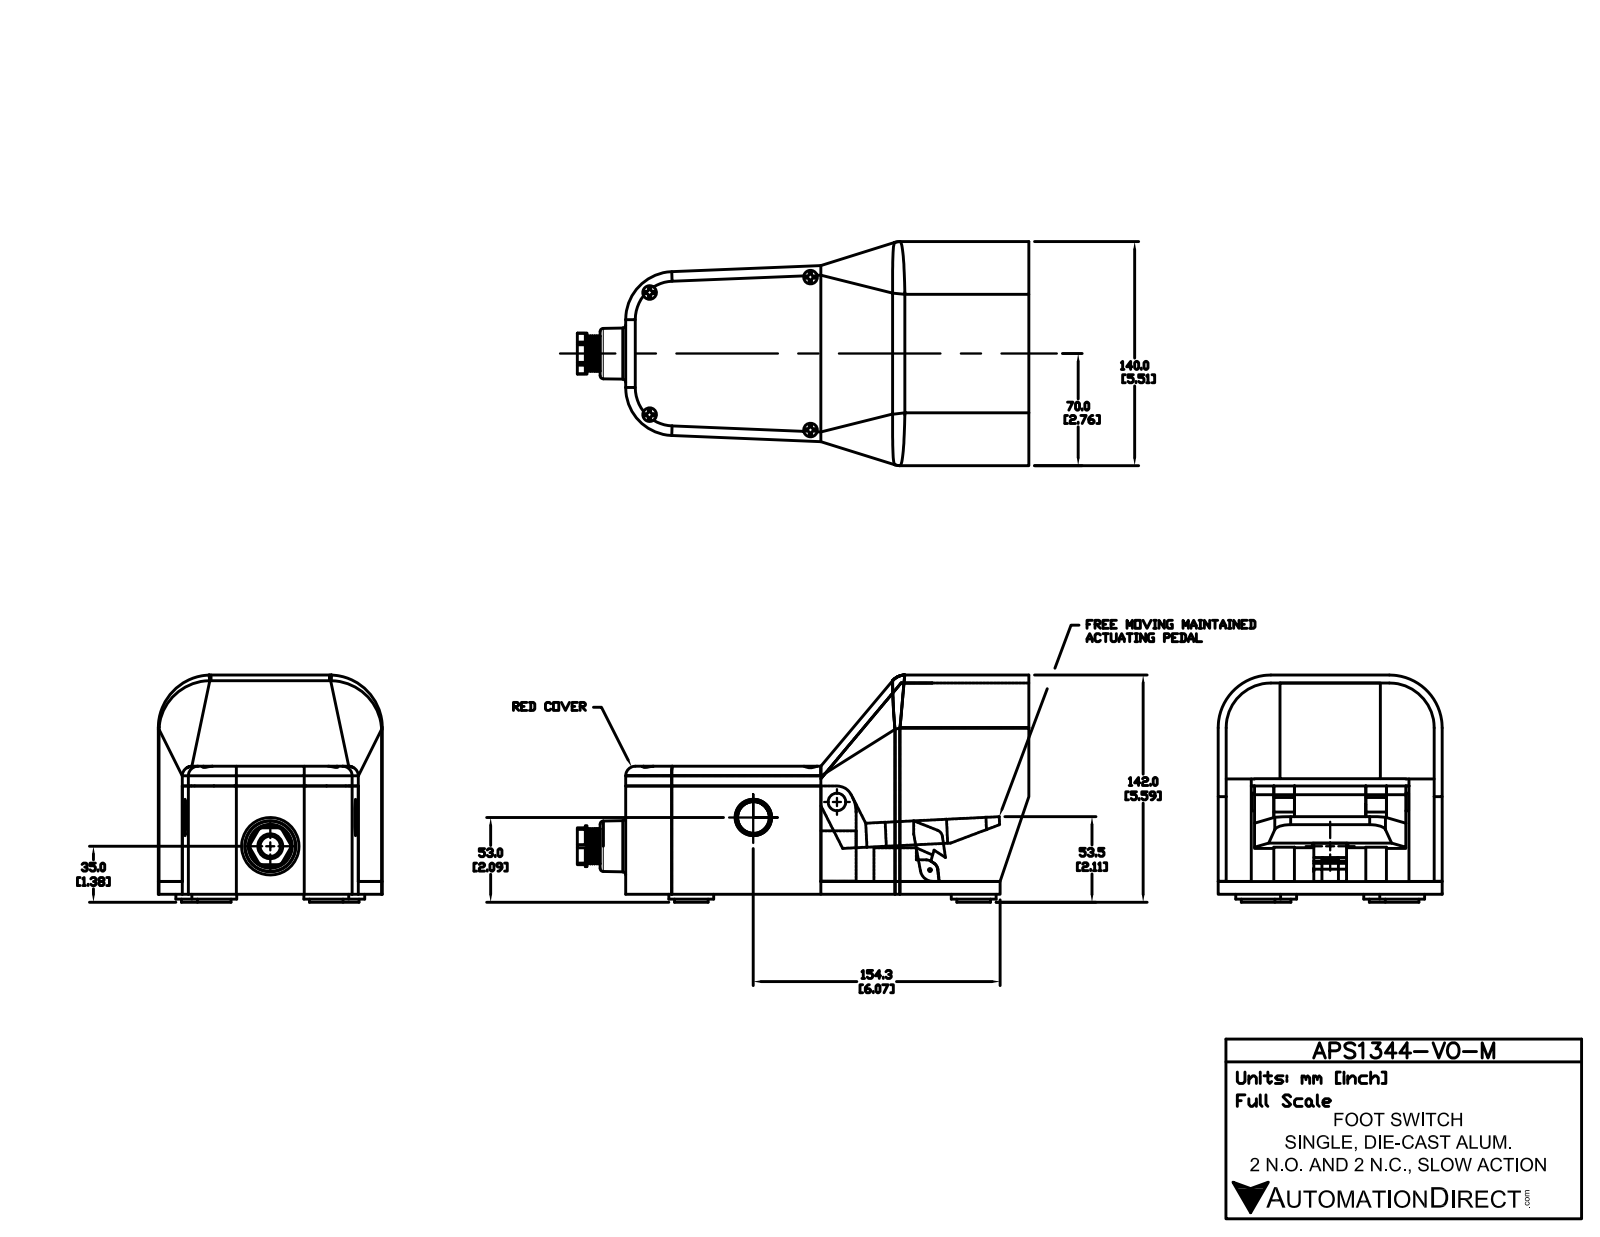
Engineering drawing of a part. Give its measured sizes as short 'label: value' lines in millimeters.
name: APS1344-V0-M
written by: SolidWorks 2015 (AUTOMOTIVE_DESIGN)
unit: mm
bodies: 19 solids, 400 faces (242 planar, 102 cylindrical, 56 other)
size: 282.25 × 142 × 140
volume: 1 555 000 mm³; area: 273 234 mm²
holes: 4× ⌀8.5, 2× ⌀22.75, 1× ⌀12.65, 1× ⌀15.6
bosses: 4× ⌀28, 4× ⌀21, 2× ⌀19.87, 1× ⌀25.5, 1× ⌀22, 1× ⌀11, 1× ⌀1.9
rounds: 16× R1, 6× R10, 4× R5, 3× R5.99, 2× R28, 2× R30, 2× R33, 1× R8
face distances: 5, 135, 8, 59.64, 67.67, 59.67, 67.64, 140, 72, 80
hole spacings: 101, 132.24, 76.3, 95.5
